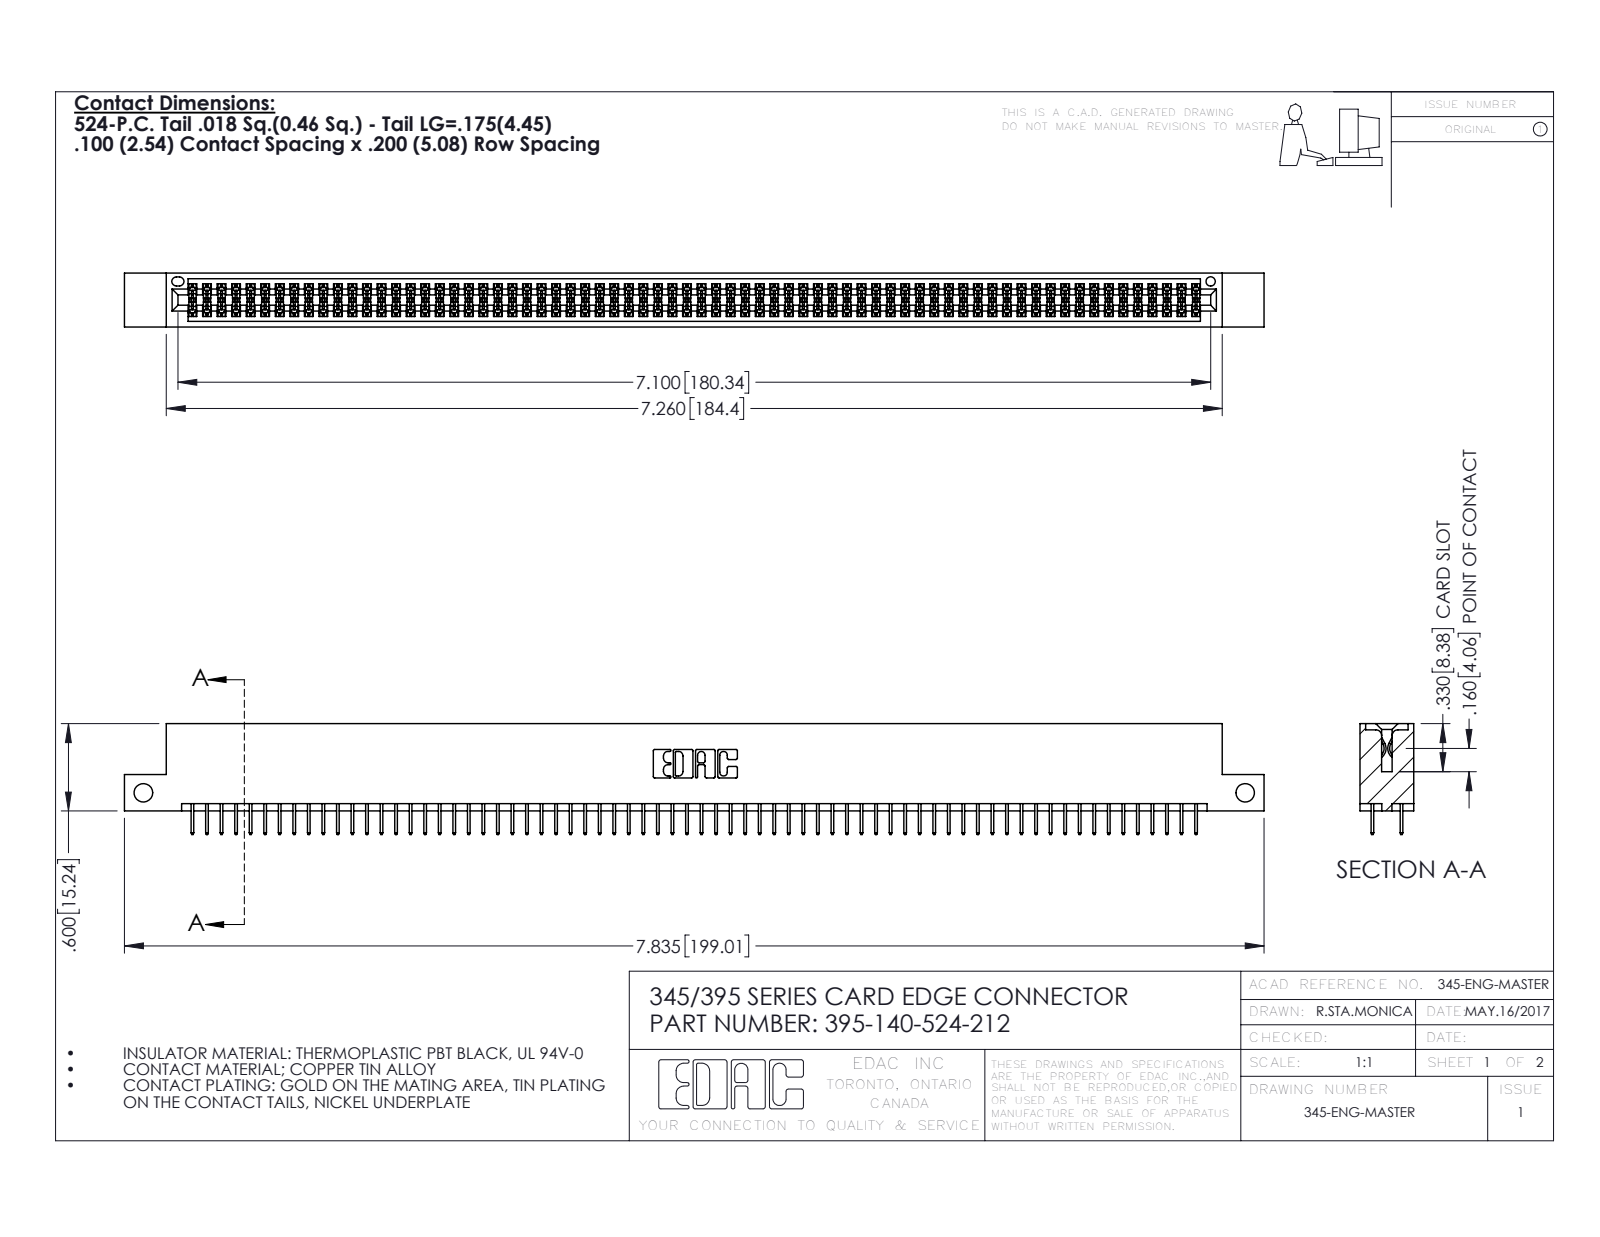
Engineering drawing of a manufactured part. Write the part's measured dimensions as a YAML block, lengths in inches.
part_name: "395-140-524-212; 345-292-001_345-293-124; 345 Part_Flush Mounting Lugs - Side Mount"
step_written_by: "SolidWorks 2016 (CONFIG_CONTROL_DESIGN)"
units: inches
bodies: {solids: 141, faces: 7686, planar: 5540, cylindrical: 2146, other: 0}
overall_size: [7.835, 0.762, 0.37]
volume: 1.177
surface_area: 43.97
round_holes:
  - {diameter: 0.128, count: 2}
  - {diameter: 0.064, count: 1}
partial_cylinders:
  - {radius: 0.006, count: 210}
  - {radius: 0.01, count: 22}
  - {radius: 0.007, count: 6}
  - {radius: 0.031, count: 6}
  - {radius: 0.026, count: 3}
  - {radius: 0.014, count: 2}
  - {radius: 0.019, count: 2}
  - {radius: 0.022, count: 2}
face_to_face_distances: [0.072, 0.298, 0.2, 0.37, 0.098, 0.272, 0.025, 0.225, 0.072, 0.175]
hole_center_spacings: [7.575]
